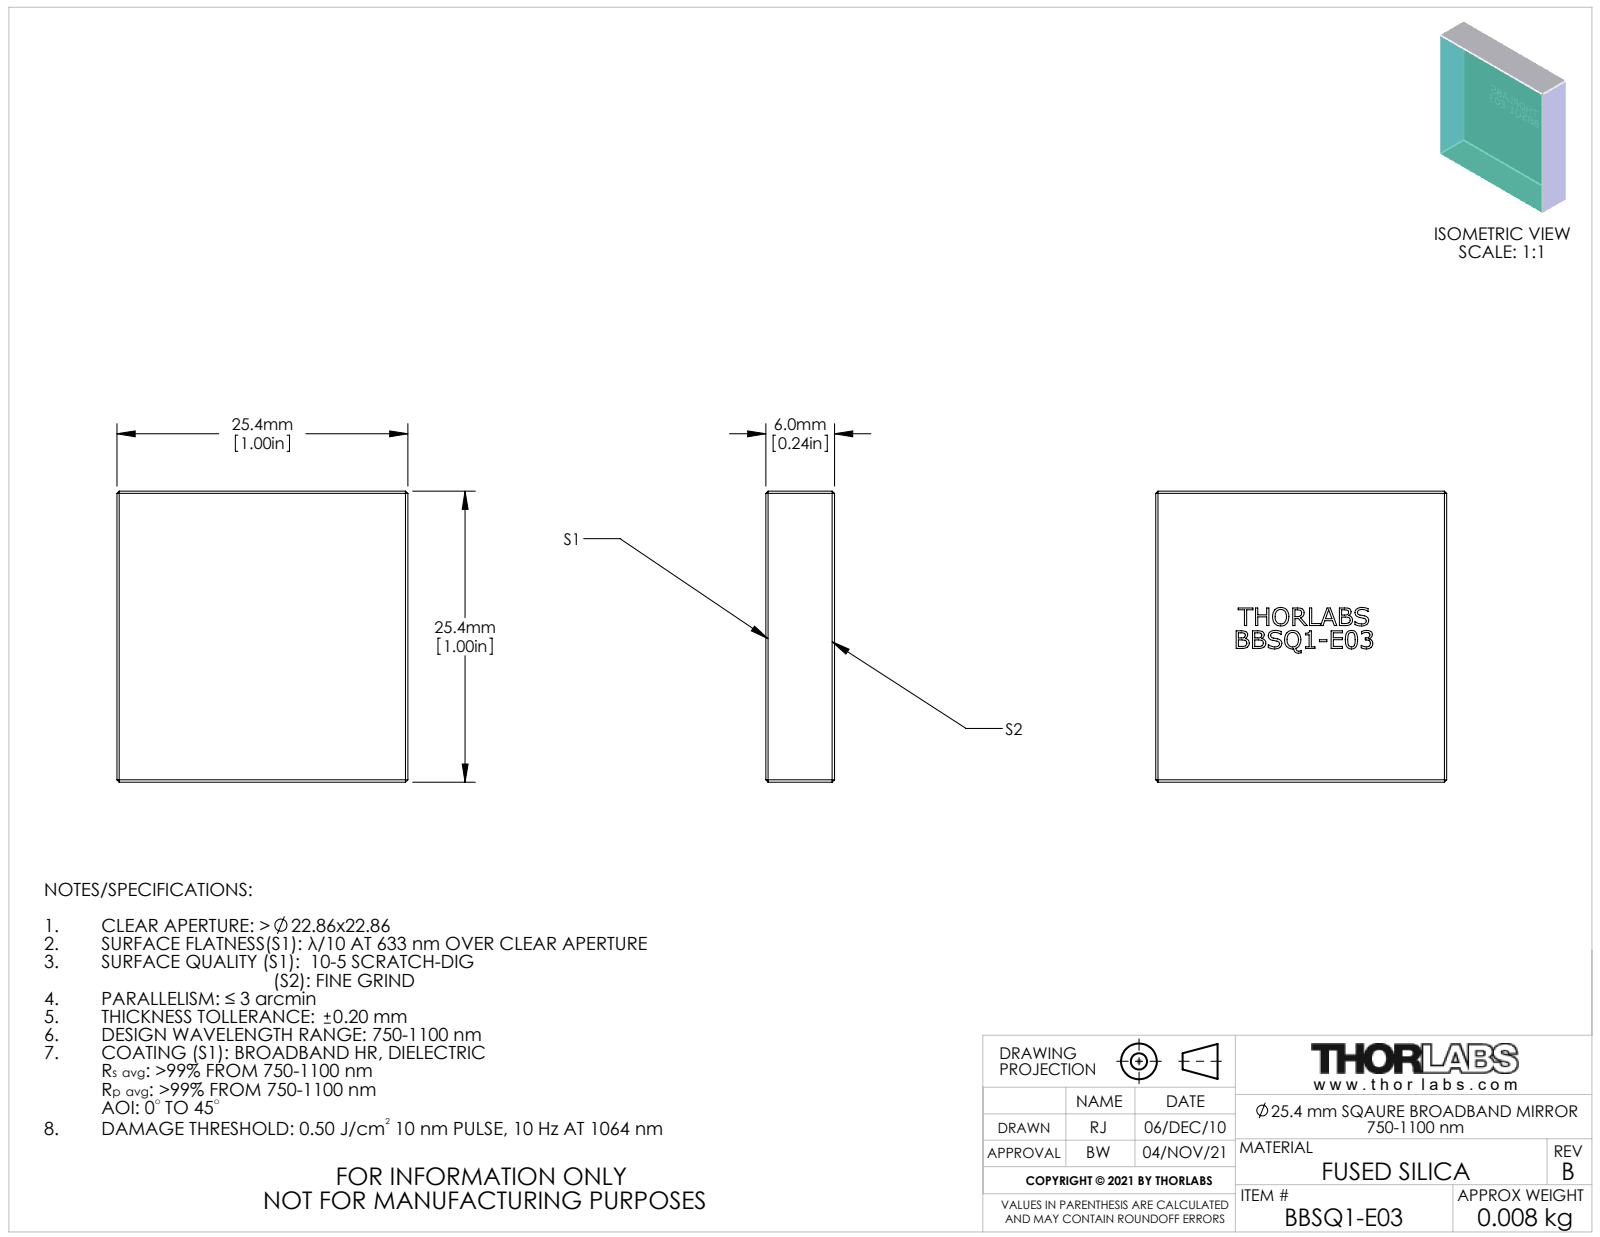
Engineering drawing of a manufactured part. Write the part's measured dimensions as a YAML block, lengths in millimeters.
part_name: "21694-E0W"
step_written_by: "SolidWorks 2009 (AUTOMOTIVE_DESIGN)"
units: millimeters
bodies: {solids: 1, faces: 304, planar: 174, cylindrical: 0, other: 130}
overall_size: [25.4, 25.4, 6]
volume: 3870
surface_area: 1874
face_to_face_distances: [6, 25.4, 21.9, 21.9, 35.6, 32.3, 2, 0.8, 2.6, 0.8]
